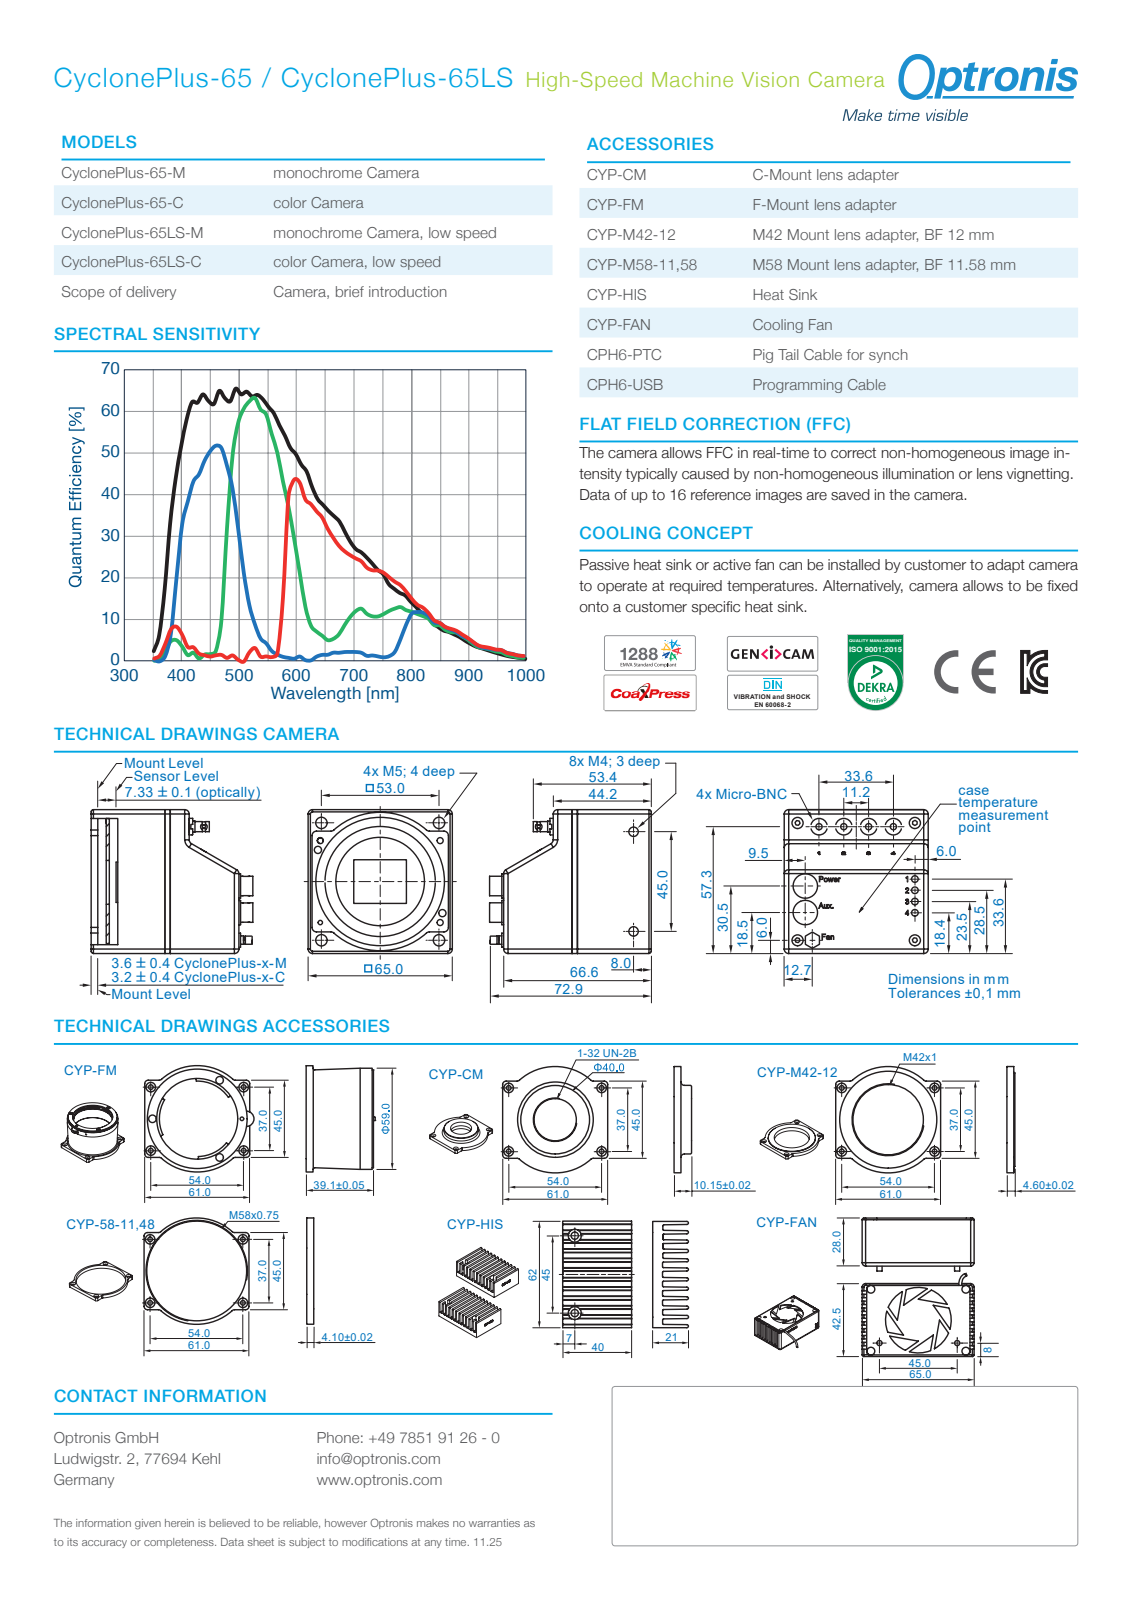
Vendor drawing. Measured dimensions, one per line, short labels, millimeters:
name: 1200-MG-46_CycloneX_Long
written by: Autodesk Inventor 2026 (AUTOMOTIVE_DESIGN)
unit: mm
bodies: 7 solids, 4272 faces (2030 planar, 1517 cylindrical, 725 other)
size: 72.9 × 65 × 65
volume: 77 699 mm³; area: 67 303 mm²
holes: 18× ⌀0.8, 10× ⌀0.5, 8× ⌀1.57, 8× ⌀2.7, 4× ⌀0.45, 4× ⌀0.46, 4× ⌀2.01, 4× ⌀2.2, 4× ⌀2.8, 4× ⌀3, 4× ⌀3.05, 4× ⌀3.24
bosses: 239× ⌀0.97, 239× ⌀0.3, 10× ⌀1.1, 8× ⌀3.8, 4× ⌀7.5, 4× ⌀6.32, 4× ⌀5.2, 4× ⌀4.55
rounds: 58× R0.2, 34× R2, 30× R3, 24× R0.17, 21× R1, 16× R0.16, 10× R0.45, 10× R0.5
face distances: 2, 63, 65, 61, 3.7, 4.6, 57.8, 4.8, 4.4, 57
hole spacings: 45.61, 11.2, 45, 22.4, 11.1, 43.21, 8.02, 8.62
